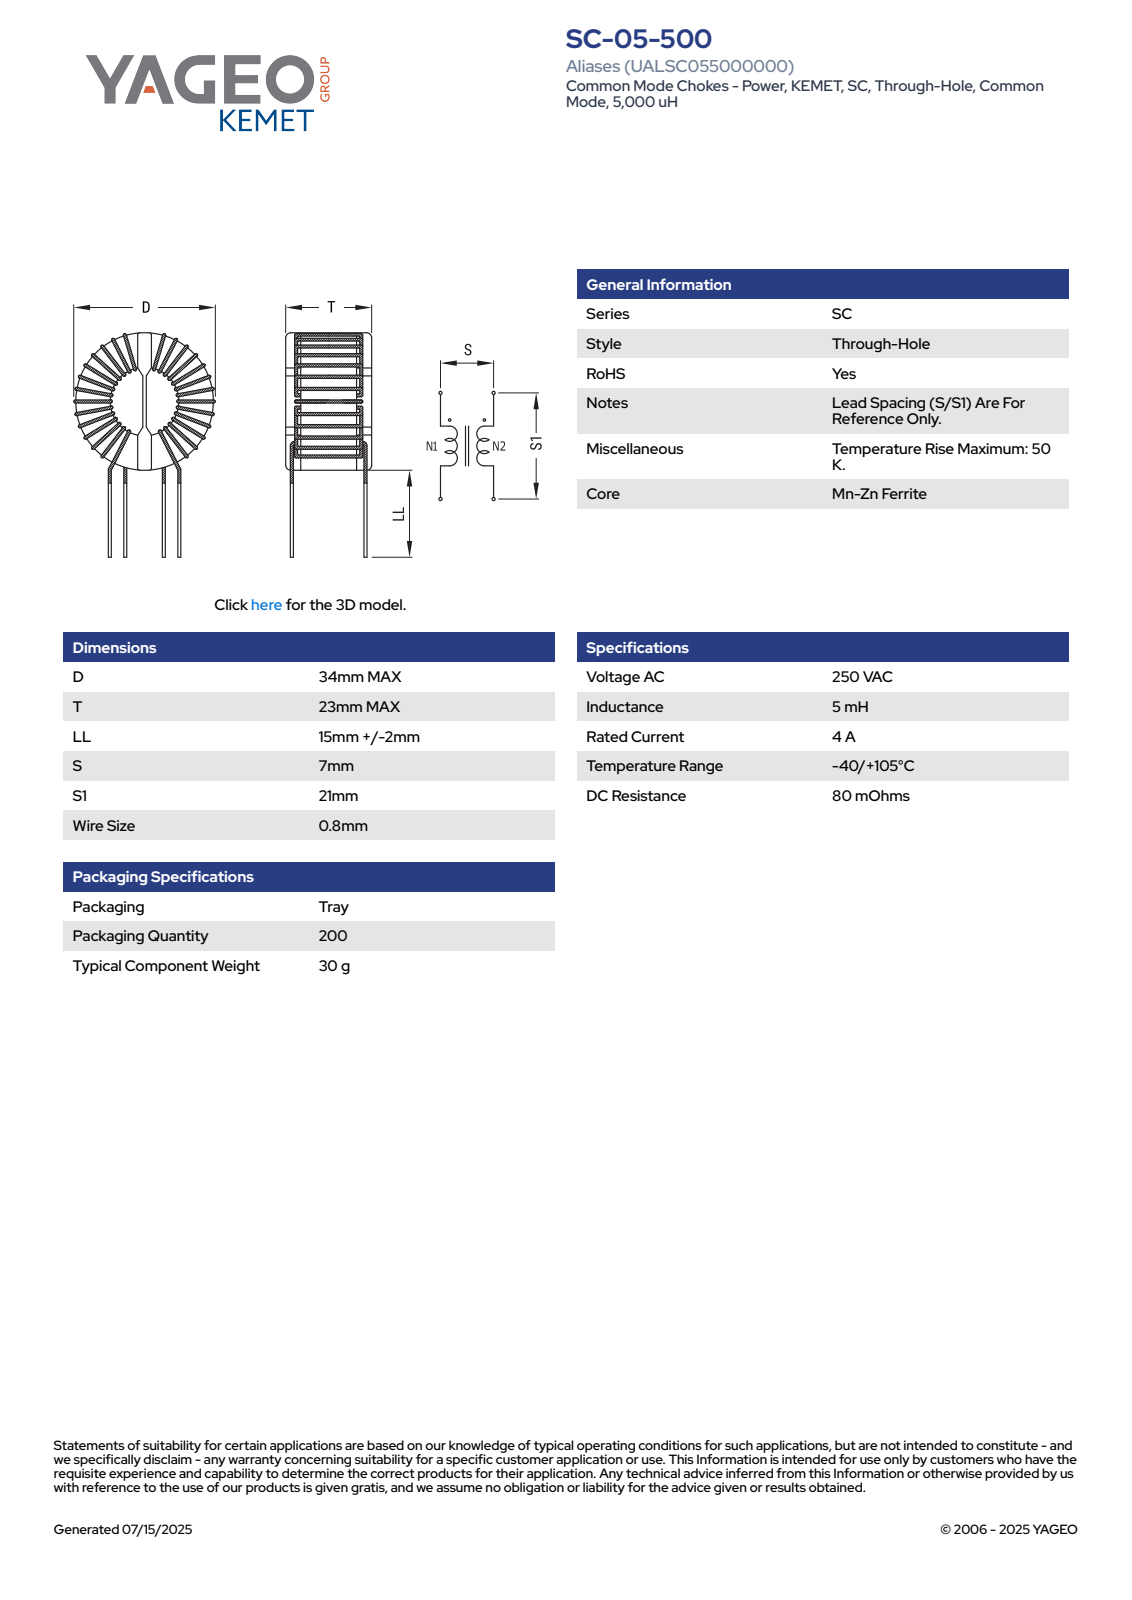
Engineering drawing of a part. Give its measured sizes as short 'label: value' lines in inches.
name: SC-05-500
written by: SolidWorks 2018 (AUTOMOTIVE_DESIGN)
unit: in
bodies: 1 solid, 269 faces (113 planar, 85 cylindrical, 71 other)
size: 1.784 × 1.339 × 0.906
volume: 0.922 in³; area: 10.05 in²
bosses: 8× ⌀0.031
rounds: 16× R0.016, 6× R0.008, 2× R0.02, 1× R0.177, 1× R0.262, 1× R0.289, 1× R0.293, 1× R0.295
face distances: 0.795, 0.047, 0.079, 0.031, 0.126, 0.098, 0.697, 0.055, 0.85, 0.752
